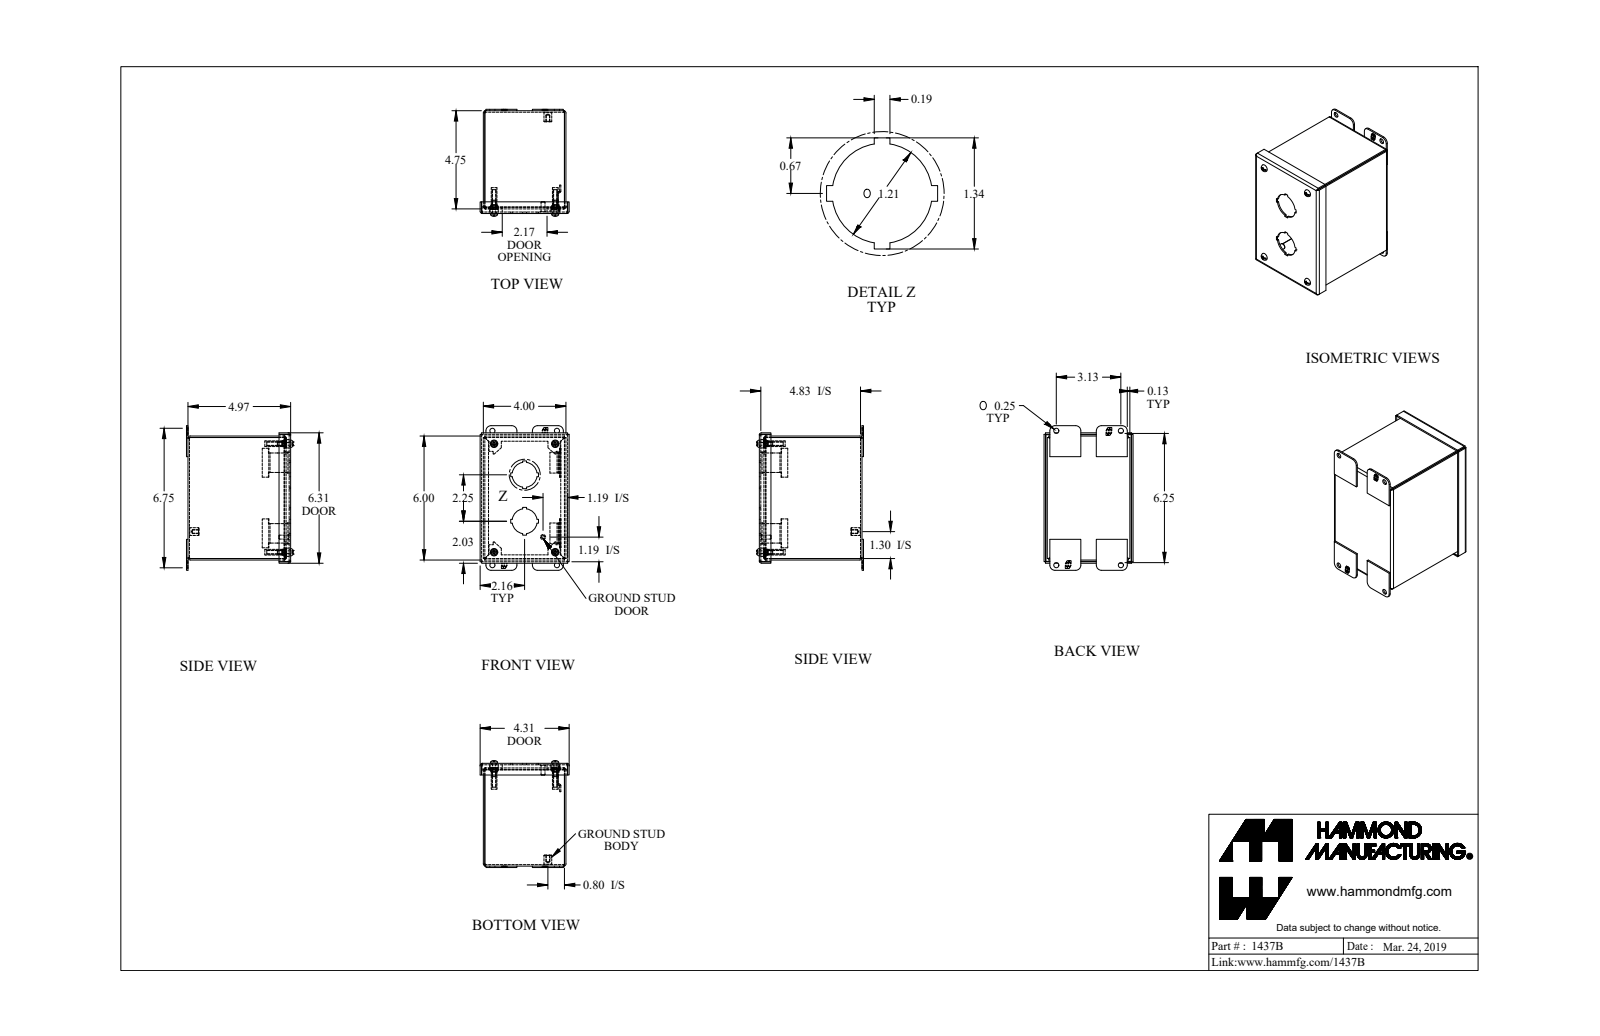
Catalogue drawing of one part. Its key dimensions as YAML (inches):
part_name: "1437B_Default"
step_written_by: "SolidWorks 2019 (CONFIG_CONTROL_DESIGN)"
units: inches
bodies: {solids: 23, faces: 747, planar: 523, cylindrical: 168, other: 56}
overall_size: [7, 5.171, 4.312]
volume: 14.02
surface_area: 376.3
round_holes:
  - {diameter: 0.25, count: 8}
  - {diameter: 0.159, count: 4}
  - {diameter: 0.406, count: 4}
  - {diameter: 1.21, count: 2}
  - {diameter: 0.156, count: 1}
round_bosses_or_shafts:
  - {diameter: 0.39, count: 4}
  - {diameter: 0.275, count: 4}
  - {diameter: 0.19, count: 4}
  - {diameter: 0.148, count: 4}
  - {diameter: 0.375, count: 1}
  - {diameter: 0.25, count: 1}
  - {diameter: 0.188, count: 1}
partial_cylinders:
  - {radius: 0.036, count: 12}
  - {radius: 0.108, count: 12}
  - {radius: 0.25, count: 8}
  - {radius: 0.029, count: 4}
  - {radius: 0.086, count: 4}
  - {radius: 0.16, count: 4}
  - {radius: 0.171, count: 4}
  - {radius: 0.125, count: 3}
face_to_face_distances: [0.072, 3.928, 4.9, 5.928, 4.972, 4, 3.856, 4.828, 0.156, 6]
hole_center_spacings: [5.875, 5.25, 3.106, 0.631, 2.107, 2.961, 3.107, 4.031]
